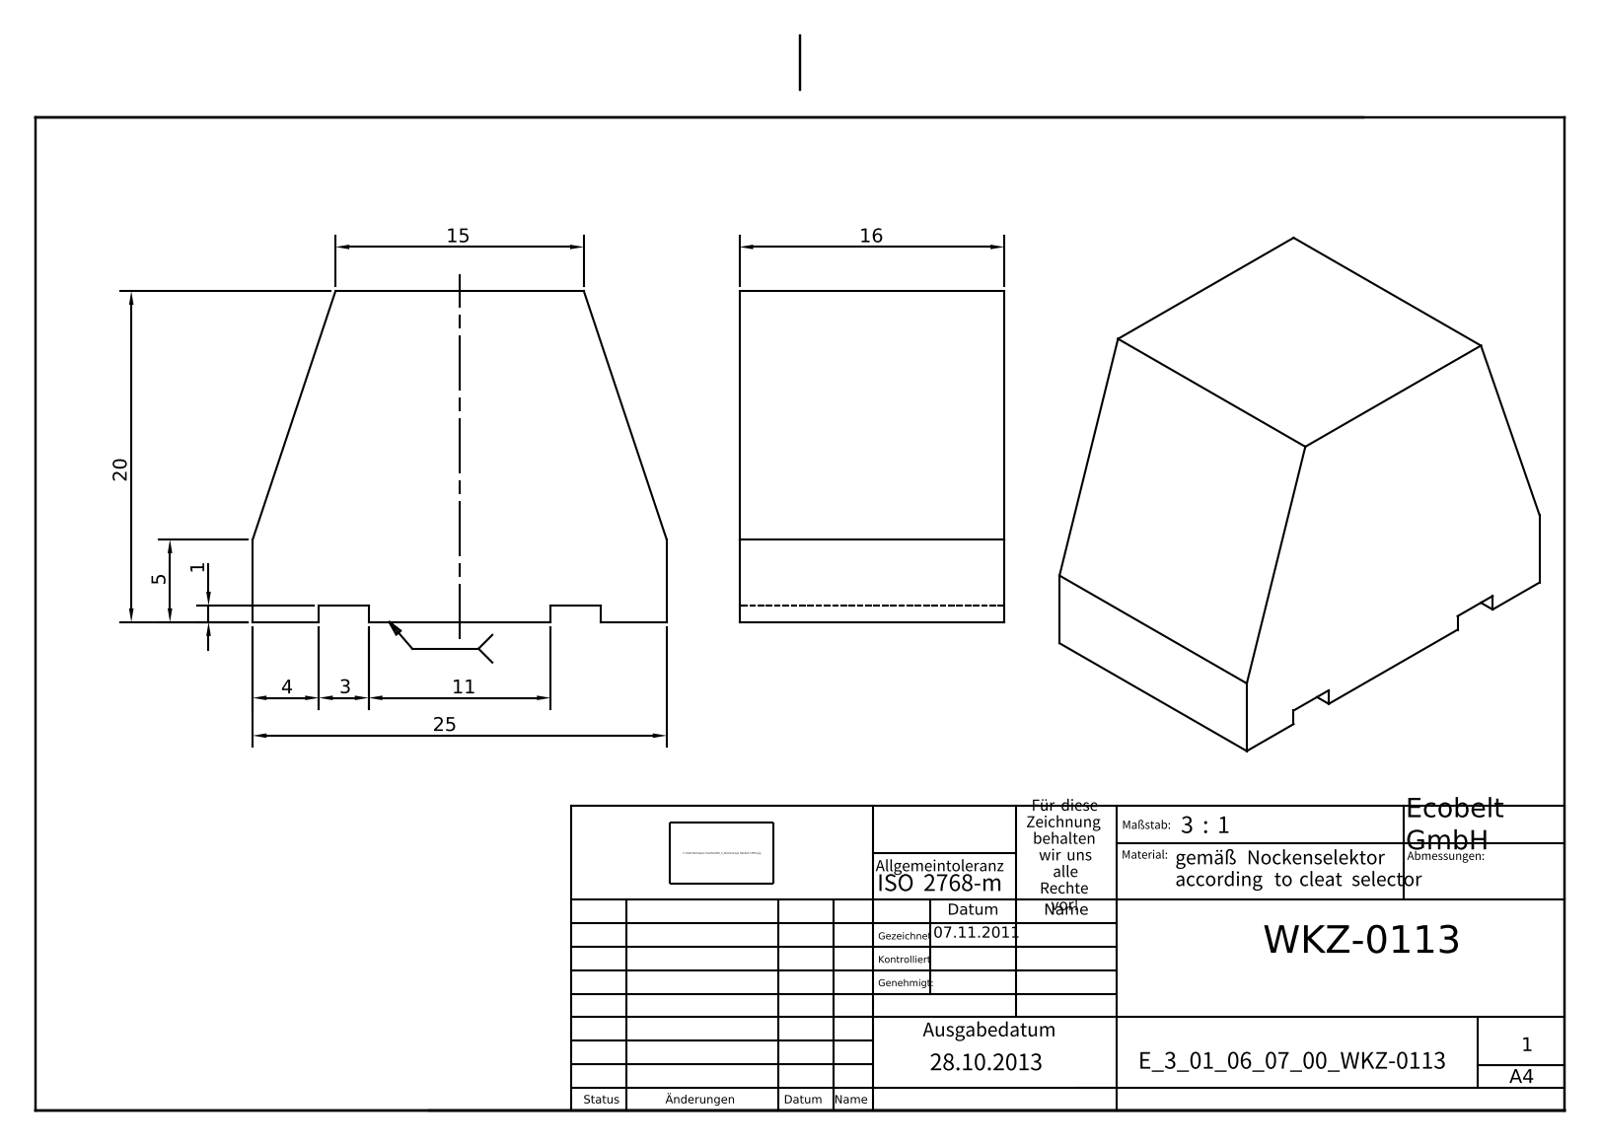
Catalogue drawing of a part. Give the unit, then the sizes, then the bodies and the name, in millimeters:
Units: millimetres
Overall size (bounding box): 25 × 20 × 16
Main face-to-face distances: 16, 20, 1, 19, 25, 4, 7, 18, 21, 3
Volume: 6 704 mm³ · Surface area: 2 208 mm²
Bodies: 1 solid, 16 faces (16 planar, 0 cylindrical, 0 other)
Part name (STEP PRODUCT): E_3_01_06_07_00_WKZ-0113
STEP written by: Autodesk Inventor 2025 (AUTOMOTIVE_DESIGN)
